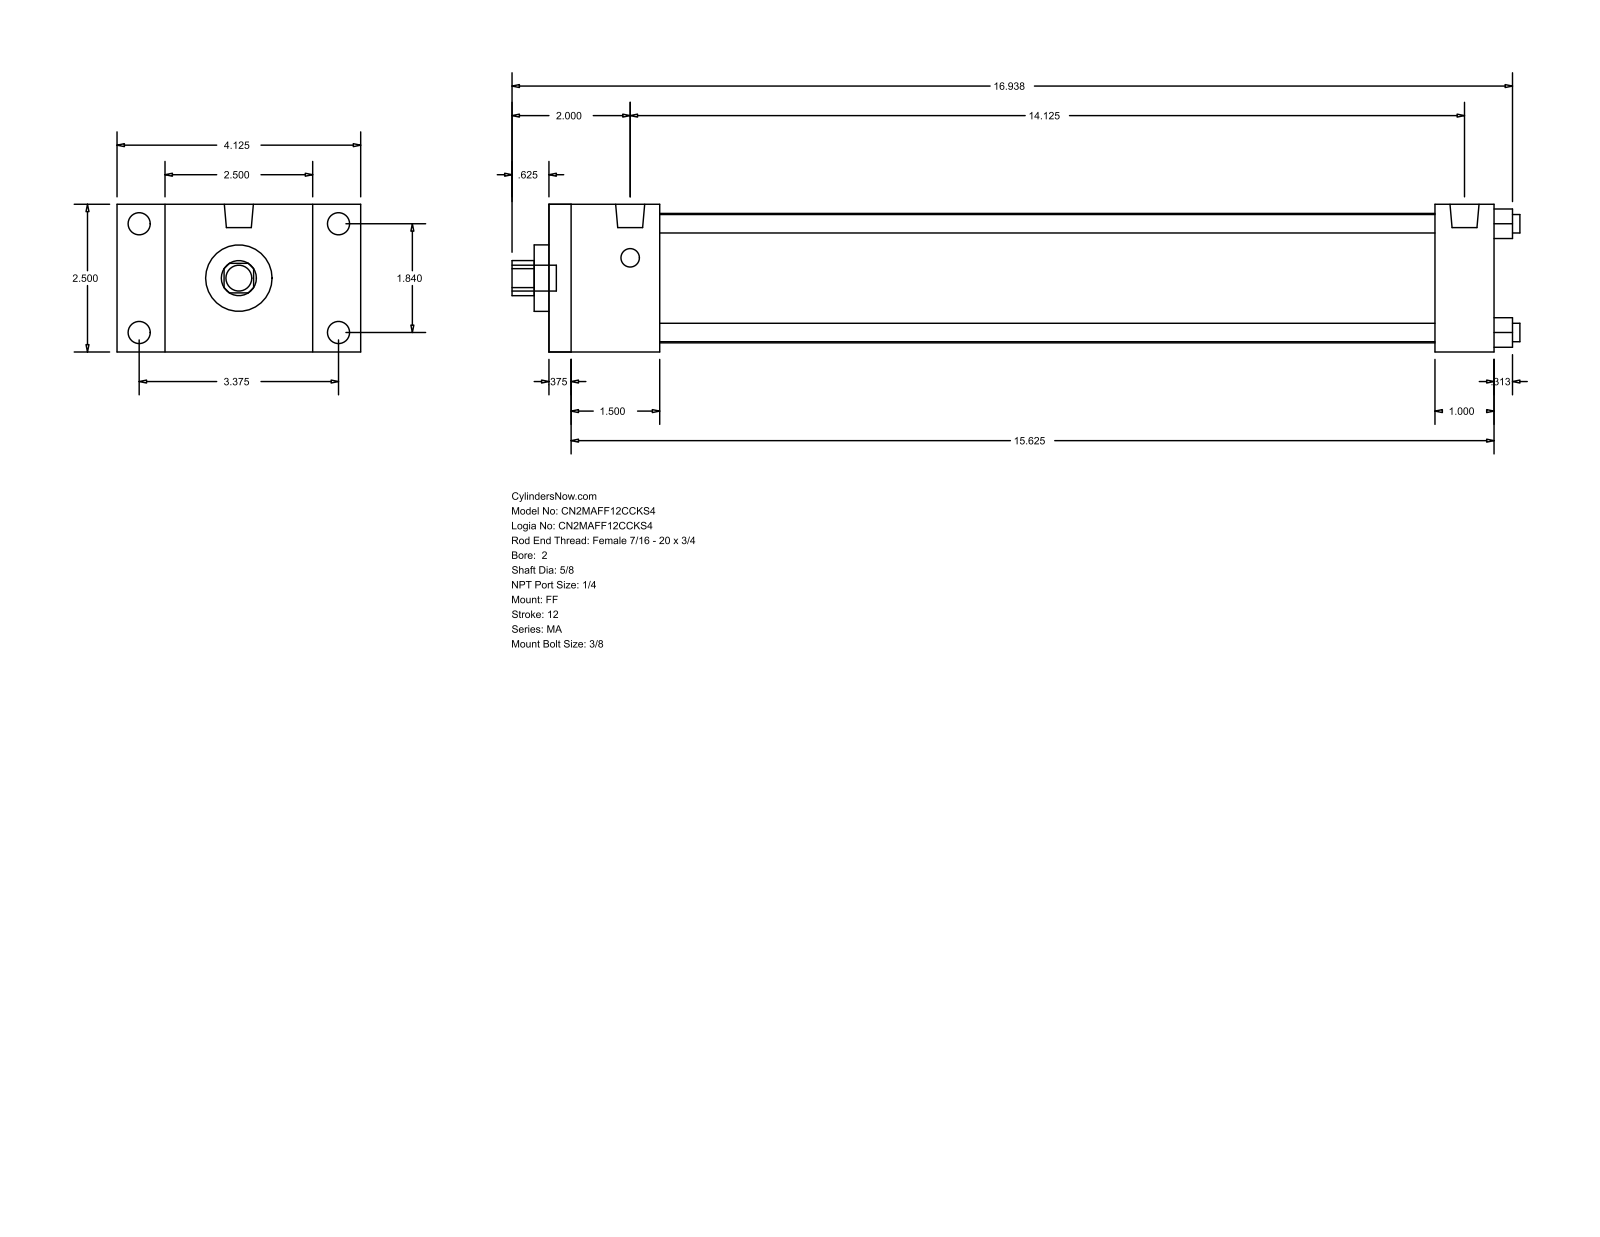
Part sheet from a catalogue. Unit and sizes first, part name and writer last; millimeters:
Units: millimetres
Overall size (bounding box): 433.39 × 104.78 × 63.5
Round holes (diameter × count): ⌀7.94 ×4, ⌀15.88 ×1, ⌀28.57 ×1, ⌀55.63 ×1
Round bosses / shafts (diameter × count): ⌀9.53 ×4, ⌀7.94 ×4, ⌀12.49 ×2, ⌀11.11 ×1
Partial cylindrical surfaces — rounded edges, fillets, slot ends (radius × count): R7.54 ×1
Main face-to-face distances: 63.5, 406.39, 9.52, 396.87, 38.1, 47.62, 381, 371.48, 333.38, 358.77
Hole centre spacings: 33.05, 46.74, 66.1
Bodies: 0 solids, 92 faces (64 planar, 28 cylindrical, 0 other)
Part name (STEP PRODUCT): MA_FF__0200_0.625
STEP written by: GSSL Pune (CONFIG_CONTROL_DESIGN)
